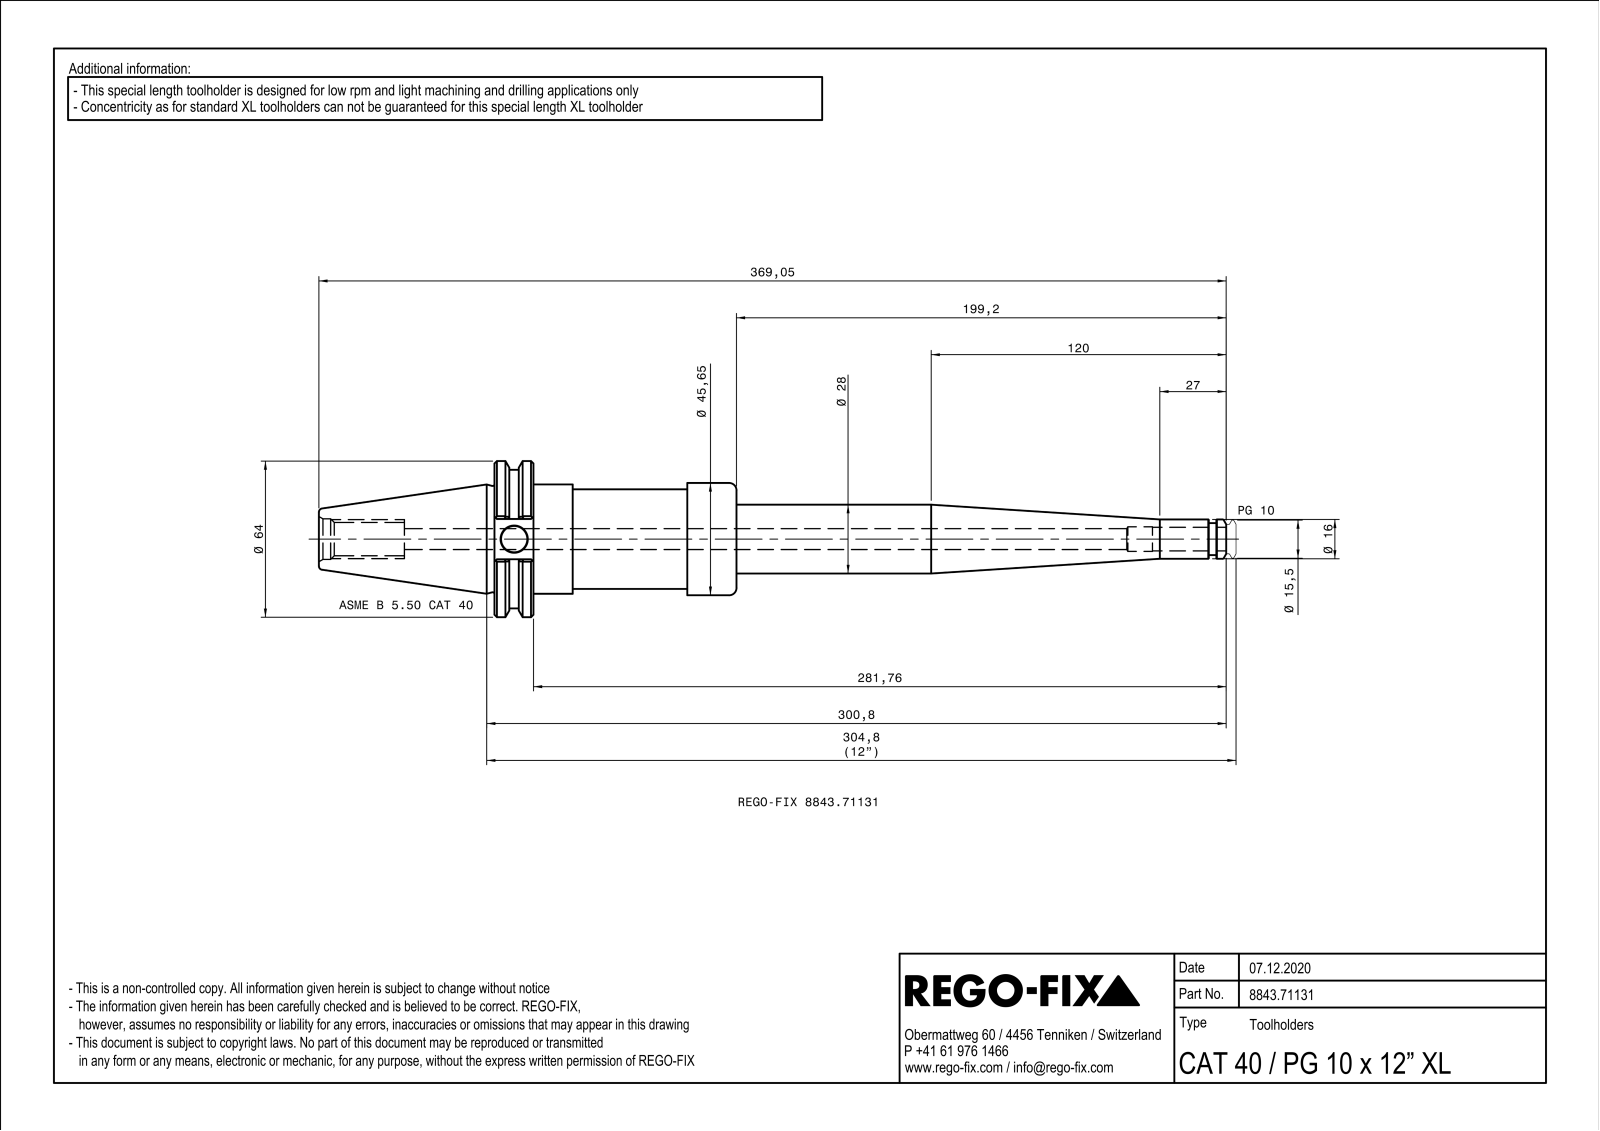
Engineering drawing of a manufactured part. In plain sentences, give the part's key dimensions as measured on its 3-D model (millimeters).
The part is named "NOCUT". Its 3-D file was written by "SIEMENS PLM Software Solid Edge ST10 (AUTOMOTIVE_DESIGN)". It is 1 solid with 155 faces: 47 planar, 35 cylindrical and 73 other. Overall it measures 369.05 by 63.5 by 60.79 millimeters. Its volume is 276 601 cubic millimeters and its surface area 62 076 square millimeters. Round holes: 1 of diameter 9, 1 of diameter 10, 1 of diameter 10.7, 1 of diameter 13.53, 1 of diameter 16.5, 1 of diameter 25, 1 of diameter 29, 1 of diameter 38.38, 1 of diameter 40.05, 1 of diameter 43.3. Round bosses or shafts: 1 of diameter 63.5, 1 of diameter 56.36, 1 of diameter 45.65, 1 of diameter 44.45, 1 of diameter 40.5, 1 of diameter 40, 1 of diameter 34, 1 of diameter 33. Partial cylindrical surfaces (rounded edges, fillets, slot ends): 4 of radius 0.5, 1 of radius 22.77. The main face-to-face distances are 15.87, 82.56, 98.43, 6, 14, 1.5, 81.06, 96.93, 20, 18.5.
